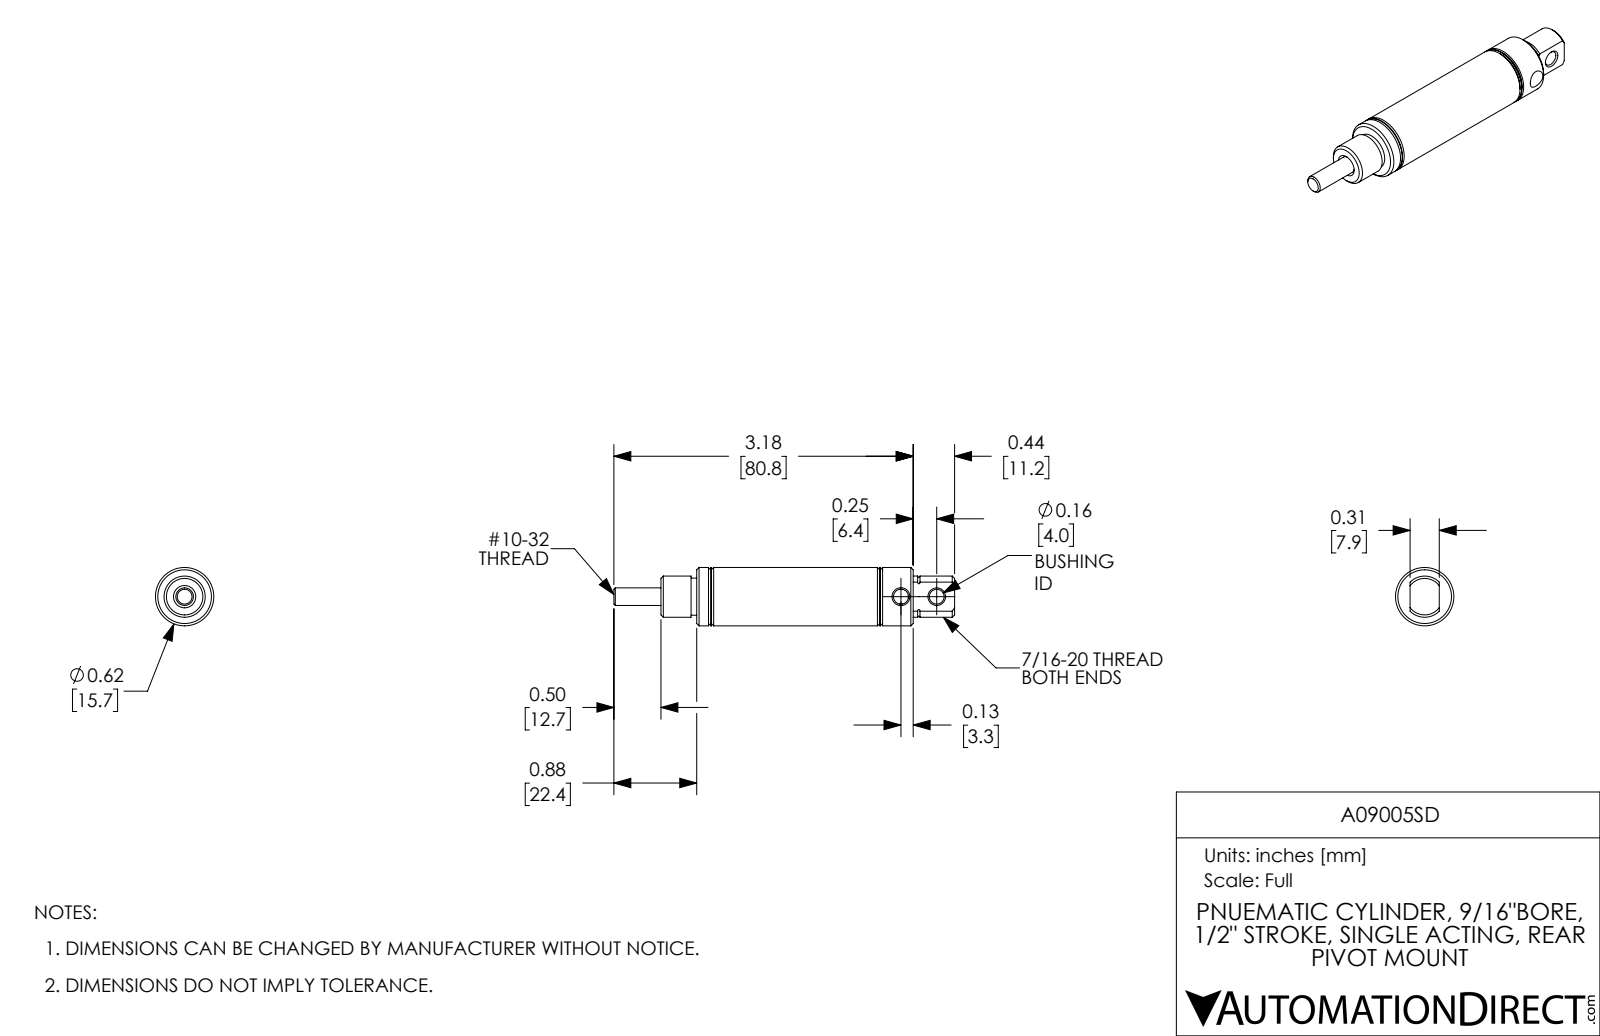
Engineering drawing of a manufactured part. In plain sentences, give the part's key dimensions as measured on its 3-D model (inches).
The part is named "A09005SD; A09005SD-Rod; A09005SD-MainBody". Its 3-D file was written by "SolidWorks 2017 (AUTOMOTIVE_DESIGN)". It is 2 solids with 94 faces: 19 planar, 38 cylindrical and 37 other. Overall it measures 3.62 by 0.62 by 0.62 inches. Its volume is 0.678 cubic inches and its surface area 12.24 square inches. Round holes: 1 of diameter 0.156, 1 of diameter 0.157, 1 of diameter 0.159, 1 of diameter 0.187, 1 of diameter 0.19, 1 of diameter 0.563. Round bosses or shafts: 1 of diameter 0.62, 1 of diameter 0.437, 1 of diameter 0.394. The main face-to-face distances are 0.5, 0.65, 1.15, 1.65, 1, 2.3, 0.31, 0.44, 1.09, 1.59. The hole center spacings are 0.38.
